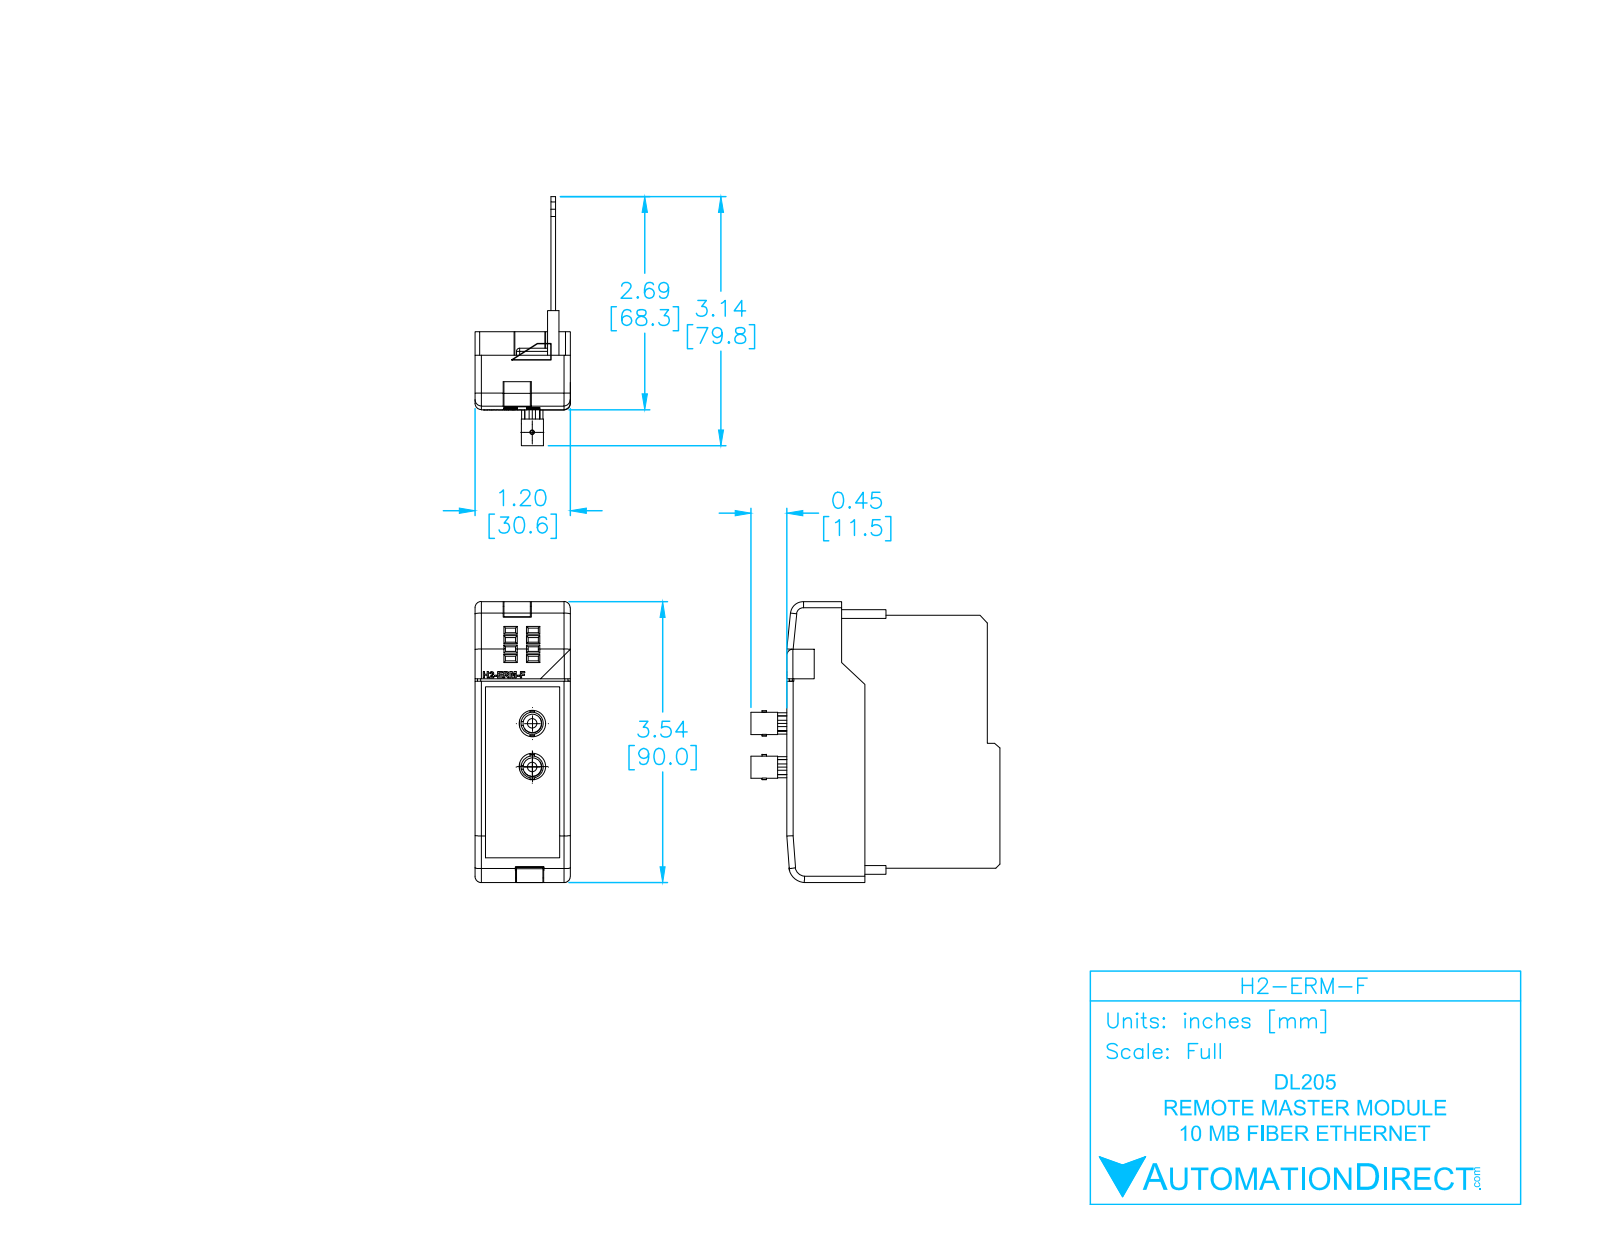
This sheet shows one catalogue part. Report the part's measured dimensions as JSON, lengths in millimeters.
{"part_name": "H2-ERM-F", "step_written_by": "SolidWorks 2009 (AUTOMOTIVE_DESIGN)", "units": "millimeters", "bodies": {"solids": 4, "faces": 470, "planar": 303, "cylindrical": 121, "other": 46}, "overall_size": [90, 79.78, 30.55], "volume_mm3": 22960, "surface_area_mm2": 30128, "round_holes": [[3, 2], [6, 2], [8.5, 2]], "round_bosses_or_shafts": [[7.08, 2], [1.4, 1]], "partial_cylinders_radius": [[0.5, 29], [1, 14], [2, 11], [0.25, 4], [2.62, 1], [3.79, 1], [4.12, 1], [5.29, 1]], "face_to_face_distances": [1.5, 4.72, 3.22, 0.5, 6.22, 29, 24.28, 25.78, 30.5, 22.78], "hole_center_spacings": [14, 13.75, 13.79, 13.96, 14.04]}
